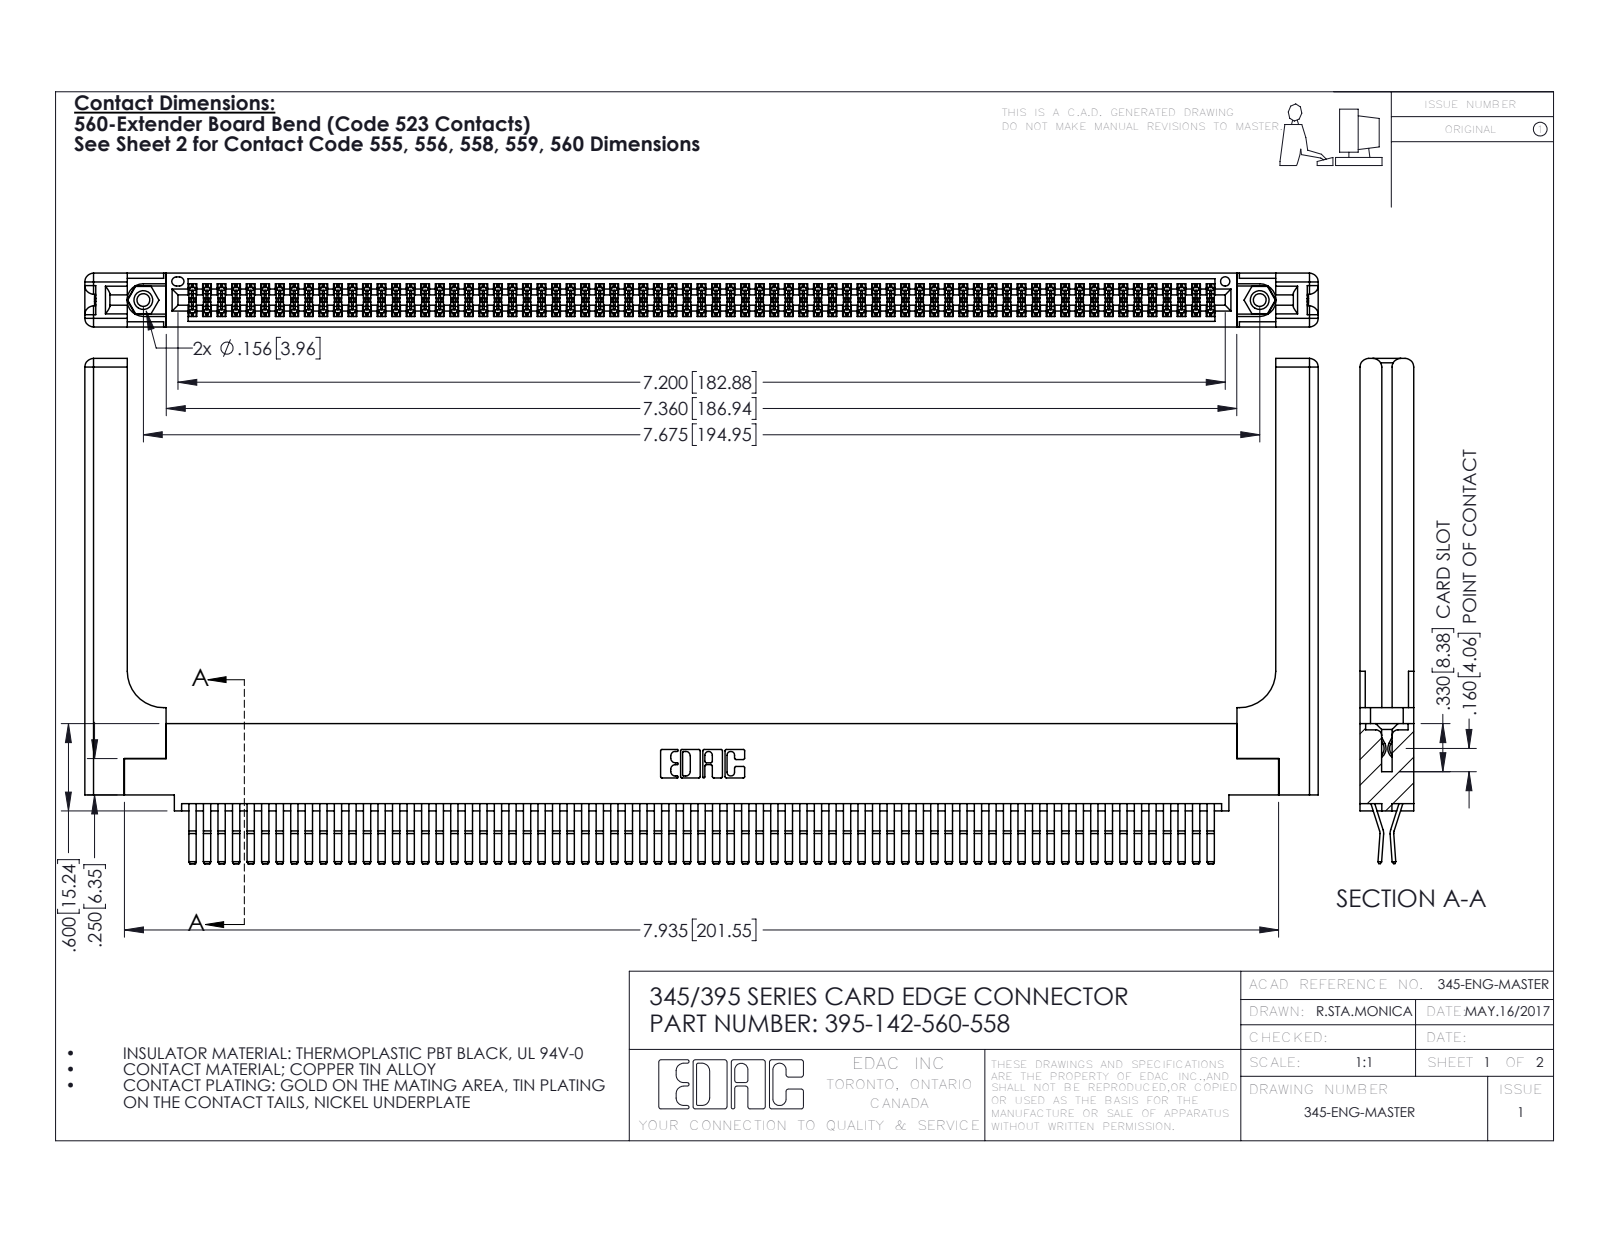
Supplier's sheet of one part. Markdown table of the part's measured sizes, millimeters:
| quantity | value |
| --- | --- |
| part name | 345-220-058_345-220-058; 345-250-001_345-250-001-102; 395-142-560-558; 345 Part_0.110 Offset - 0.156 Dia-TH (+1 more) |
| STEP written by | SolidWorks 2016 (CONFIG_CONTROL_DESIGN) |
| units | millimeters |
| bodies | 147 solids, 7770 faces (4918 planar, 2792 cylindrical, 60 other) |
| overall size | 215.4 × 88.2 × 9.4 |
| volume | 30 530 mm³ |
| surface area | 40 700 mm² |
| round holes (diameter × count) | 2.3 × 2, 3.2 × 2, 4 × 2, 1.6 × 1 |
| round bosses / shafts (diameter × count) | 3.9 × 2 |
| partial cylindrical surfaces (radius × count) | 0.2 × 213, 0.3 × 22, 1.5 × 16, 0.2 × 6, 0.8 × 6, 0.7 × 3, 0.3 × 2, 0.4 × 2 |
| main face-to-face distances | 1.8, 7.6, 0.6, 9.4, 2.5, 6.9, 5.1, 5.7, 4.4, 3.8 |
| hole center spacings | 6.9, 189, 194.9 |
